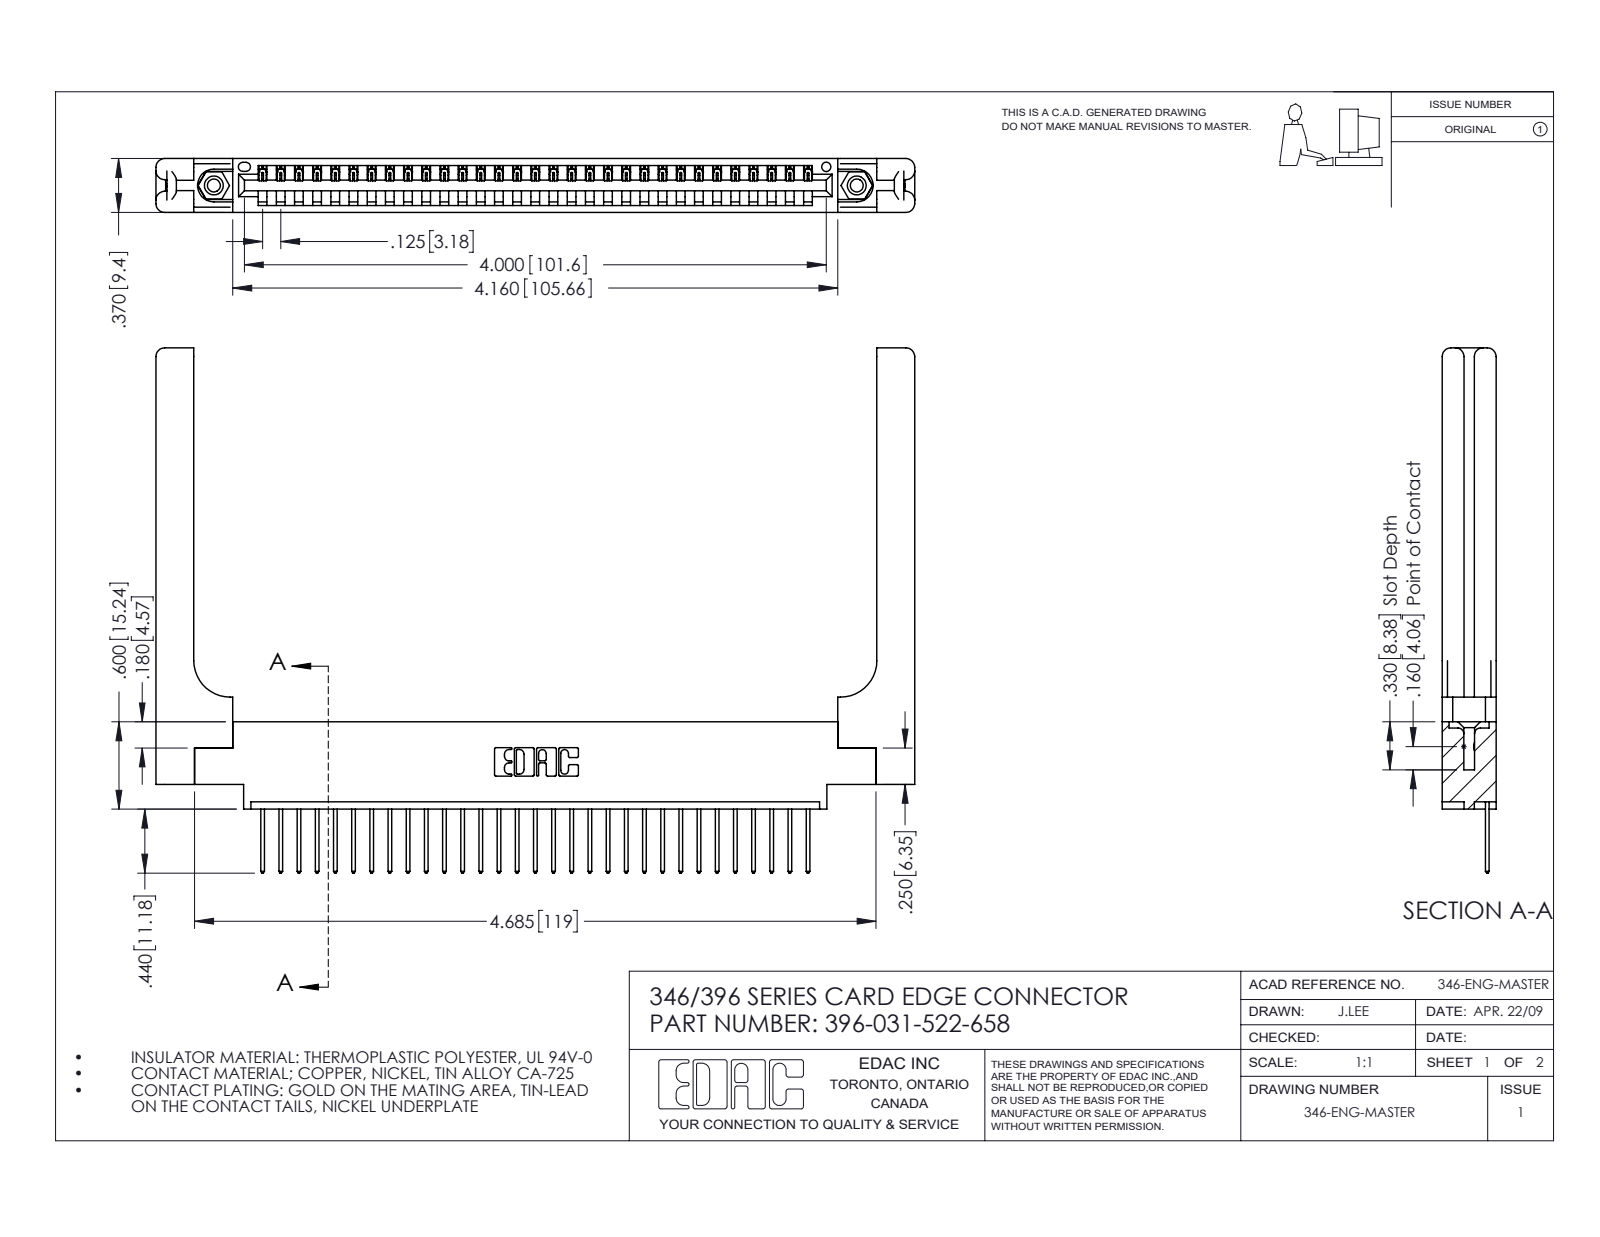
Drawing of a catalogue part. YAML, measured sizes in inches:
part_name: "396-031-522-658; 345-292-001_345-293-122; 346-220-058_345-220-058; 346 Part_0.170 Offset - 0.156 Dia-TH (+1 more)"
step_written_by: "SolidWorks 2016 (CONFIG_CONTROL_DESIGN)"
units: inches
bodies: {solids: 36, faces: 2180, planar: 1468, cylindrical: 652, other: 60}
overall_size: [5.216, 3.61, 0.37]
volume: 1.219
surface_area: 32.38
round_holes:
  - {diameter: 0.089, count: 2}
  - {diameter: 0.125, count: 2}
  - {diameter: 0.156, count: 2}
  - {diameter: 0.064, count: 1}
round_bosses_or_shafts:
  - {diameter: 0.155, count: 2}
partial_cylinders:
  - {radius: 0.006, count: 62}
  - {radius: 0.01, count: 62}
  - {radius: 0.01, count: 22}
  - {radius: 0.06, count: 16}
  - {radius: 0.007, count: 6}
  - {radius: 0.031, count: 6}
  - {radius: 0.026, count: 3}
  - {radius: 0.03, count: 2}
face_to_face_distances: [0.37, 0.072, 0.048, 0.322, 0.148, 0.15, 0.25, 0.298, 0.025, 0.222]
hole_center_spacings: [0.246, 4.212, 4.42]
